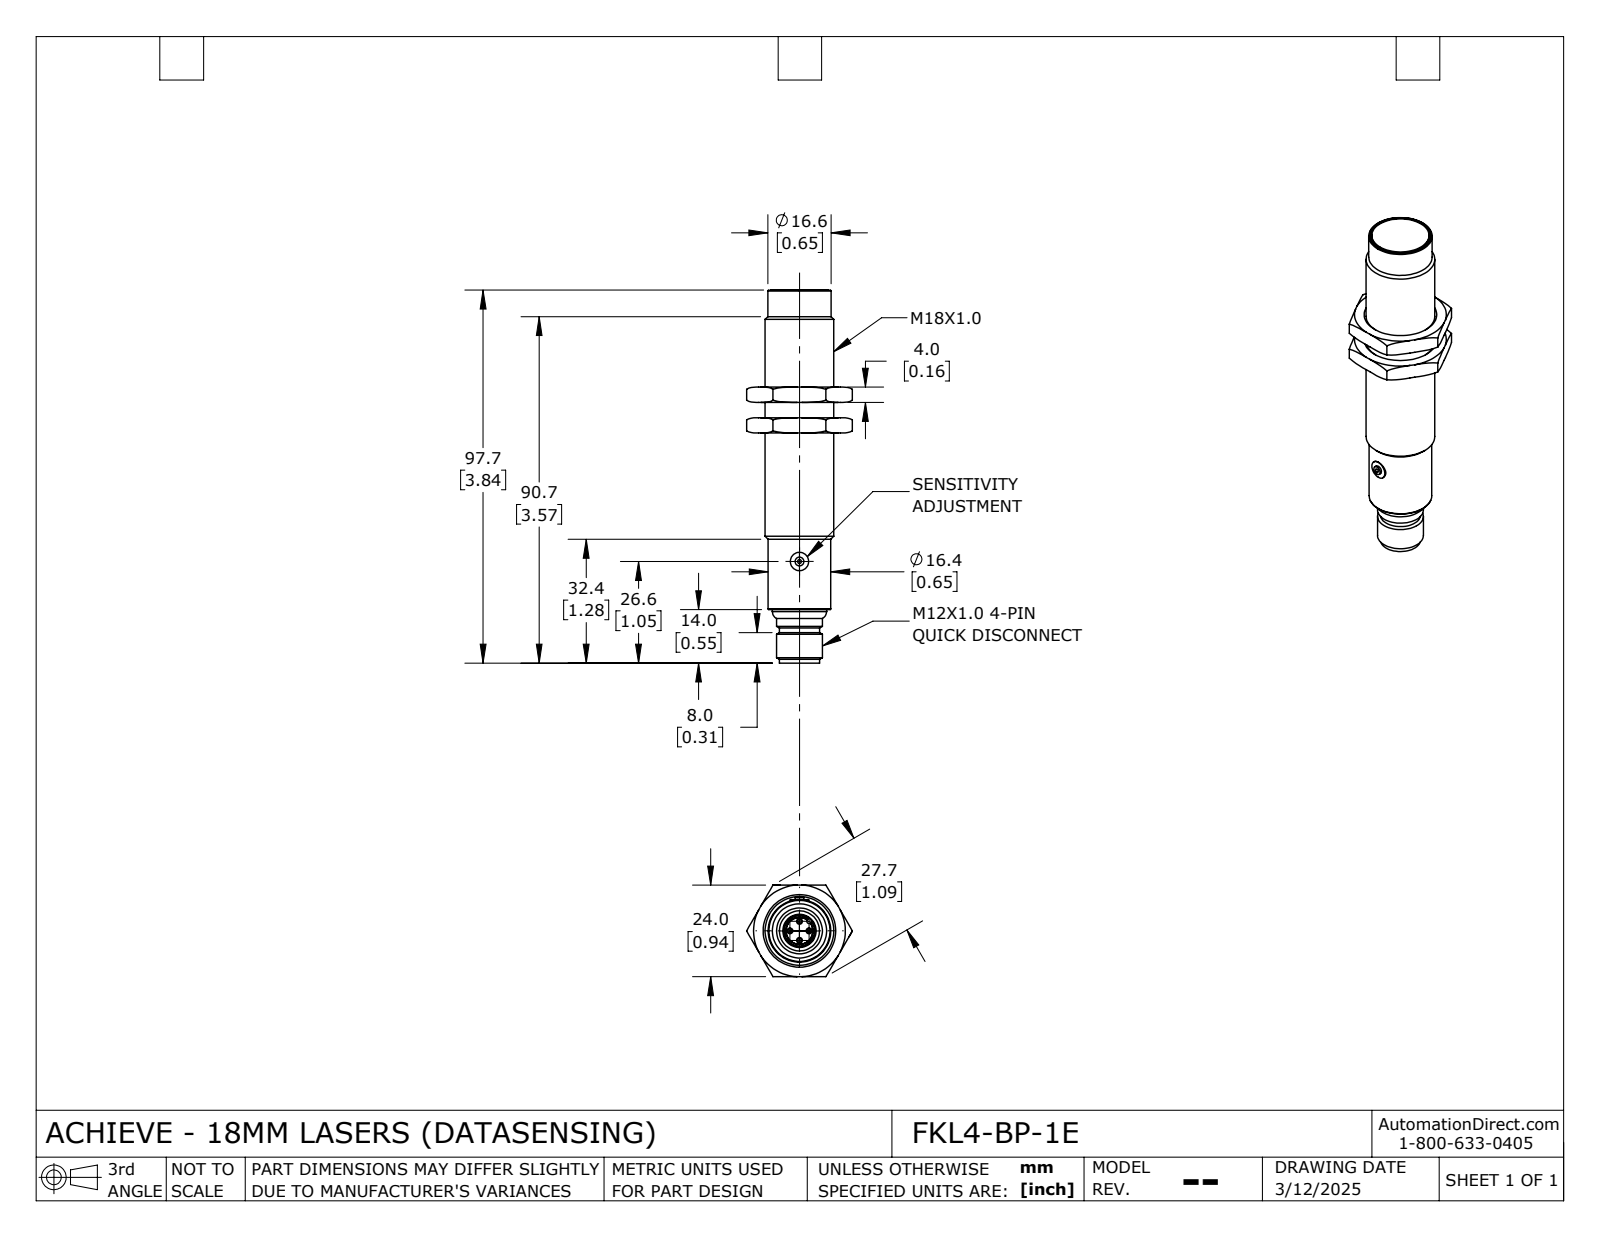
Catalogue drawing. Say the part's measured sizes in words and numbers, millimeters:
The part is named "FKL4-BP-1E_Default". Its 3-D file was written by "SolidWorks 2024 (CONFIG_CONTROL_DESIGN)". It is 3 solids with 121 faces: 43 planar, 29 cylindrical and 49 other. Overall it measures 97.6 by 27.7 by 24 millimeters. Its volume is 23 010 cubic millimeters and its surface area 9 071 square millimeters. Round holes: 1 of diameter 4.7, 1 of diameter 7.1, 1 of diameter 8.3, 1 of diameter 14.9, 1 of diameter 18. Round bosses or shafts: 4 of diameter 1, 1 of diameter 16.6, 1 of diameter 16.4, 1 of diameter 15, 1 of diameter 14.8, 1 of diameter 14.2, 1 of diameter 12, 1 of diameter 10.5. Partial cylindrical surfaces (rounded edges, fillets, slot ends): 2 of radius 0.5, 1 of radius 0.6, 1 of radius 7.5. The main face-to-face distances are 4, 8, 24, 2.4, 2.5, 30.9, 31, 33.4, 22.9, 23.
